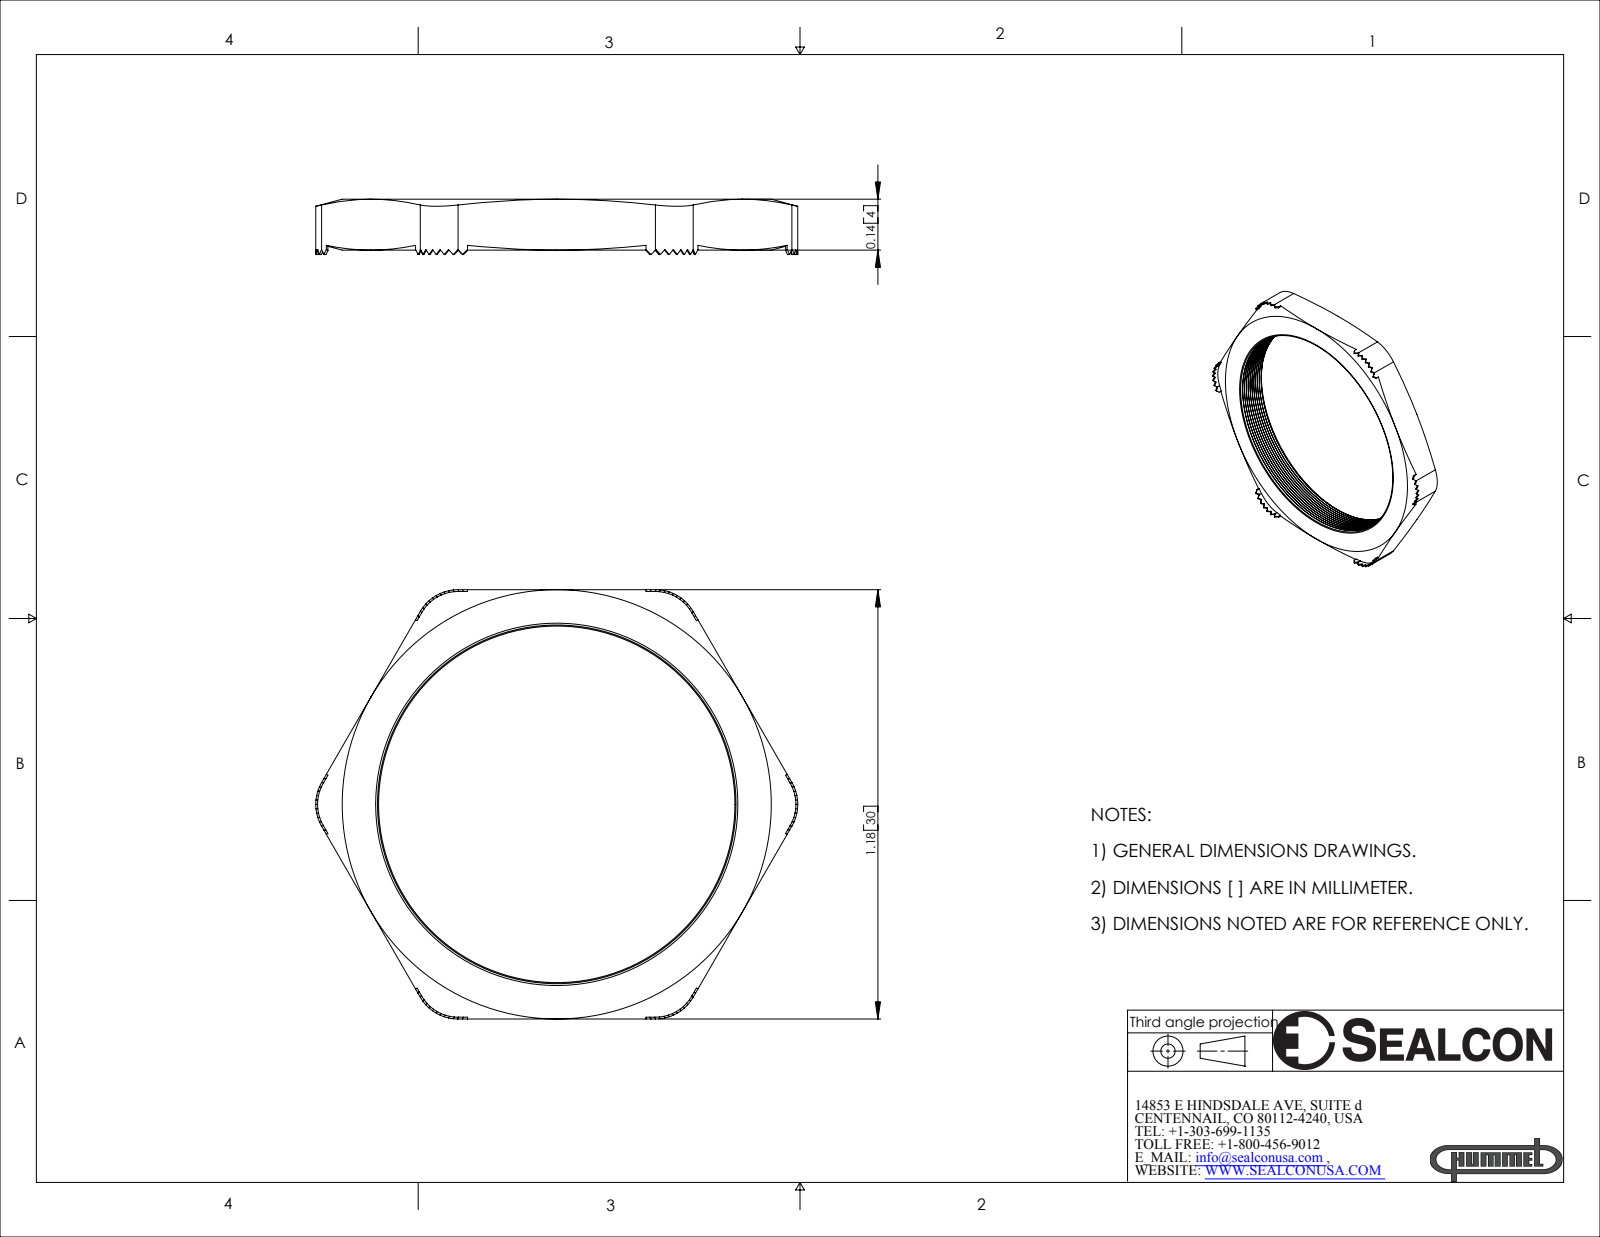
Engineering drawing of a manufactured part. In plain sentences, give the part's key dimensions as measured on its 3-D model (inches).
The part is named "NM-25-BE". Its 3-D file was written by "SolidWorks 2007 (CONFIG_CONTROL_DESIGN)". It is 1 solid with 218 faces: 116 planar, 36 cylindrical and 66 other. Overall it measures 1.325 by 1.18 by 0.152 inches. Its volume is 0.059 cubic inches and its surface area 2.265 square inches. Round holes: 1 of diameter 0.98. Partial cylindrical surfaces (rounded edges, fillets, slot ends): 6 of radius 0.115, 6 of radius 0.12. The main face-to-face distances are 0.14, 1.18, 1.175, 0.018, 1.17, 0.036, 0.035, 0.054, 0.09, 0.072.
